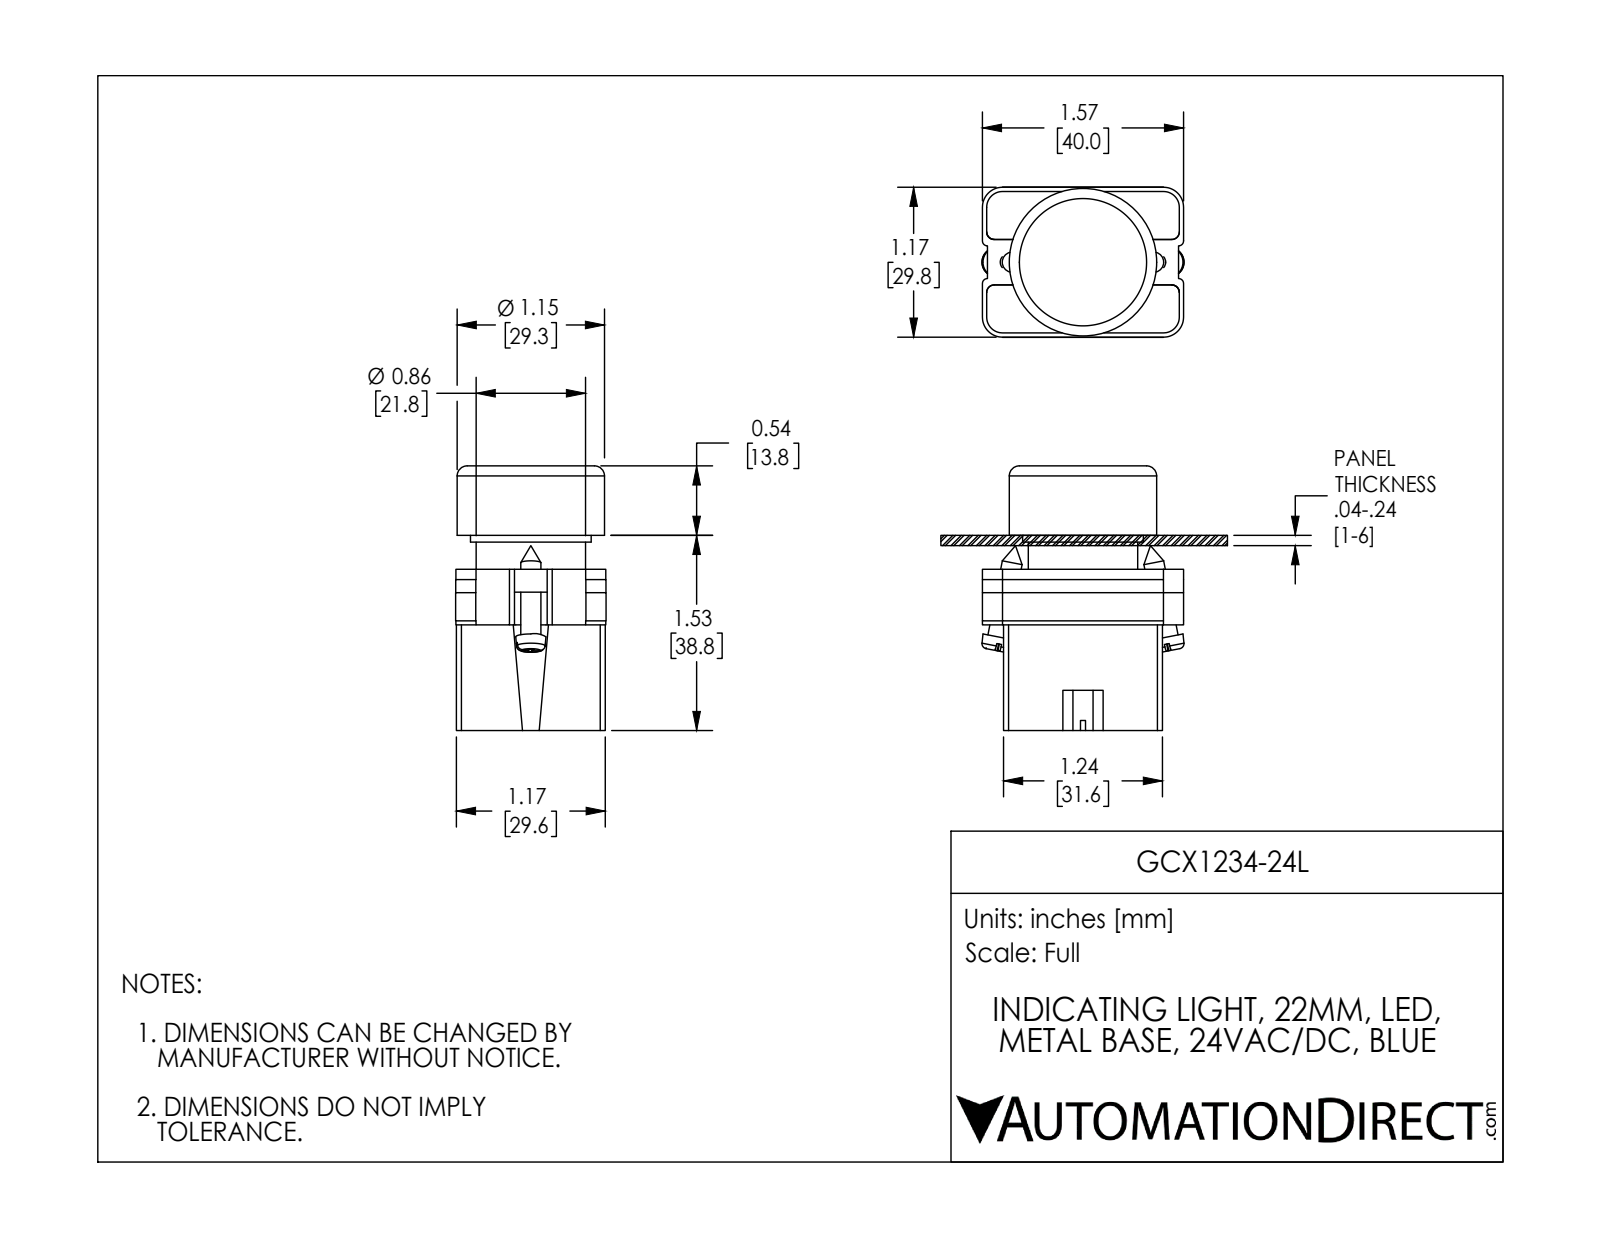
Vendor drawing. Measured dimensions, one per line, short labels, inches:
name: ecx1029; ECX1050; GCX1234-24L; GCX1234L OPERATOR
written by: SolidWorks 2016 (AUTOMOTIVE_DESIGN)
unit: in
bodies: 7 solids, 339 faces (178 planar, 134 cylindrical, 27 other)
size: 2.071 × 1.581 × 1.177
volume: 2.268 in³; area: 31.19 in²
holes: 2× ⌀0.124, 2× ⌀0.13, 1× ⌀0.197, 1× ⌀0.469, 1× ⌀0.852, 1× ⌀0.878, 1× ⌀0.888, 1× ⌀1.102
bosses: 4× ⌀0.157, 1× ⌀1.154, 1× ⌀1.092, 1× ⌀0.945, 1× ⌀0.856, 1× ⌀0.78, 1× ⌀0.504
rounds: 24× R0.059, 12× R0.041, 12× R0.124, 12× R0.157, 8× R0.039, 2× R0.128, 1× R0.392, 1× R0.398
face distances: 0.86, 1.244, 0.827, 1.687, 1.136, 0.033, 1.963, 0.276, 0.031, 1.165
